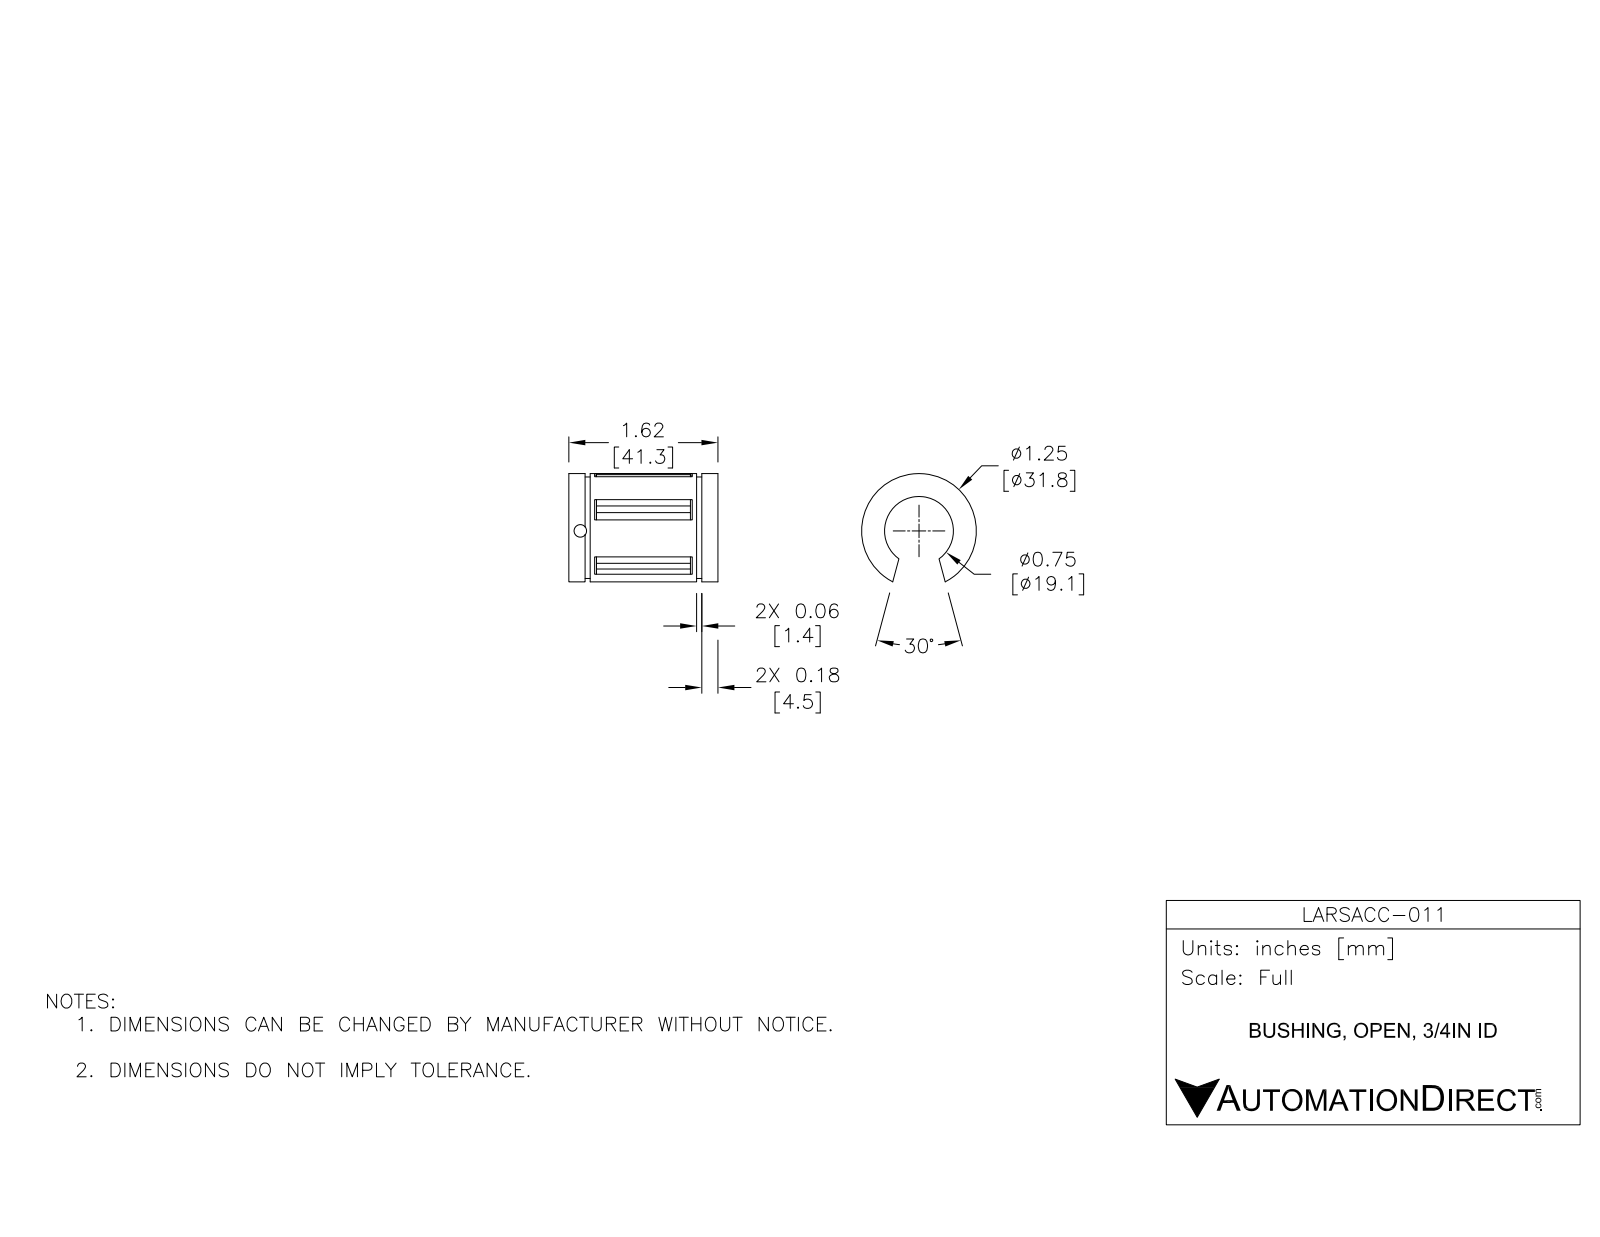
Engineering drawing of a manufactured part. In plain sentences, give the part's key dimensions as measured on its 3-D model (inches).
The part is named "LARSACC-011". Its 3-D file was written by "SolidWorks 2015 (AUTOMOTIVE_DESIGN)". It is 1 solid with 77 faces: 40 planar, 35 cylindrical and 2 other. Overall it measures 1.625 by 1.25 by 1.181 inches. Its volume is 1.044 cubic inches and its surface area 11.17 square inches. Round holes: 1 of diameter 0.75. Round bosses or shafts: 1 of diameter 1.25, 1 of diameter 1.176. Partial cylindrical surfaces (rounded edges, fillets, slot ends): 6 of radius 0.517, 5 of radius 0.615. The main face-to-face distances are 1.625, 1.216, 0.056, 0.232, 1.393, 1.448, 0.177, 1.393, 1.16, 0.233.
